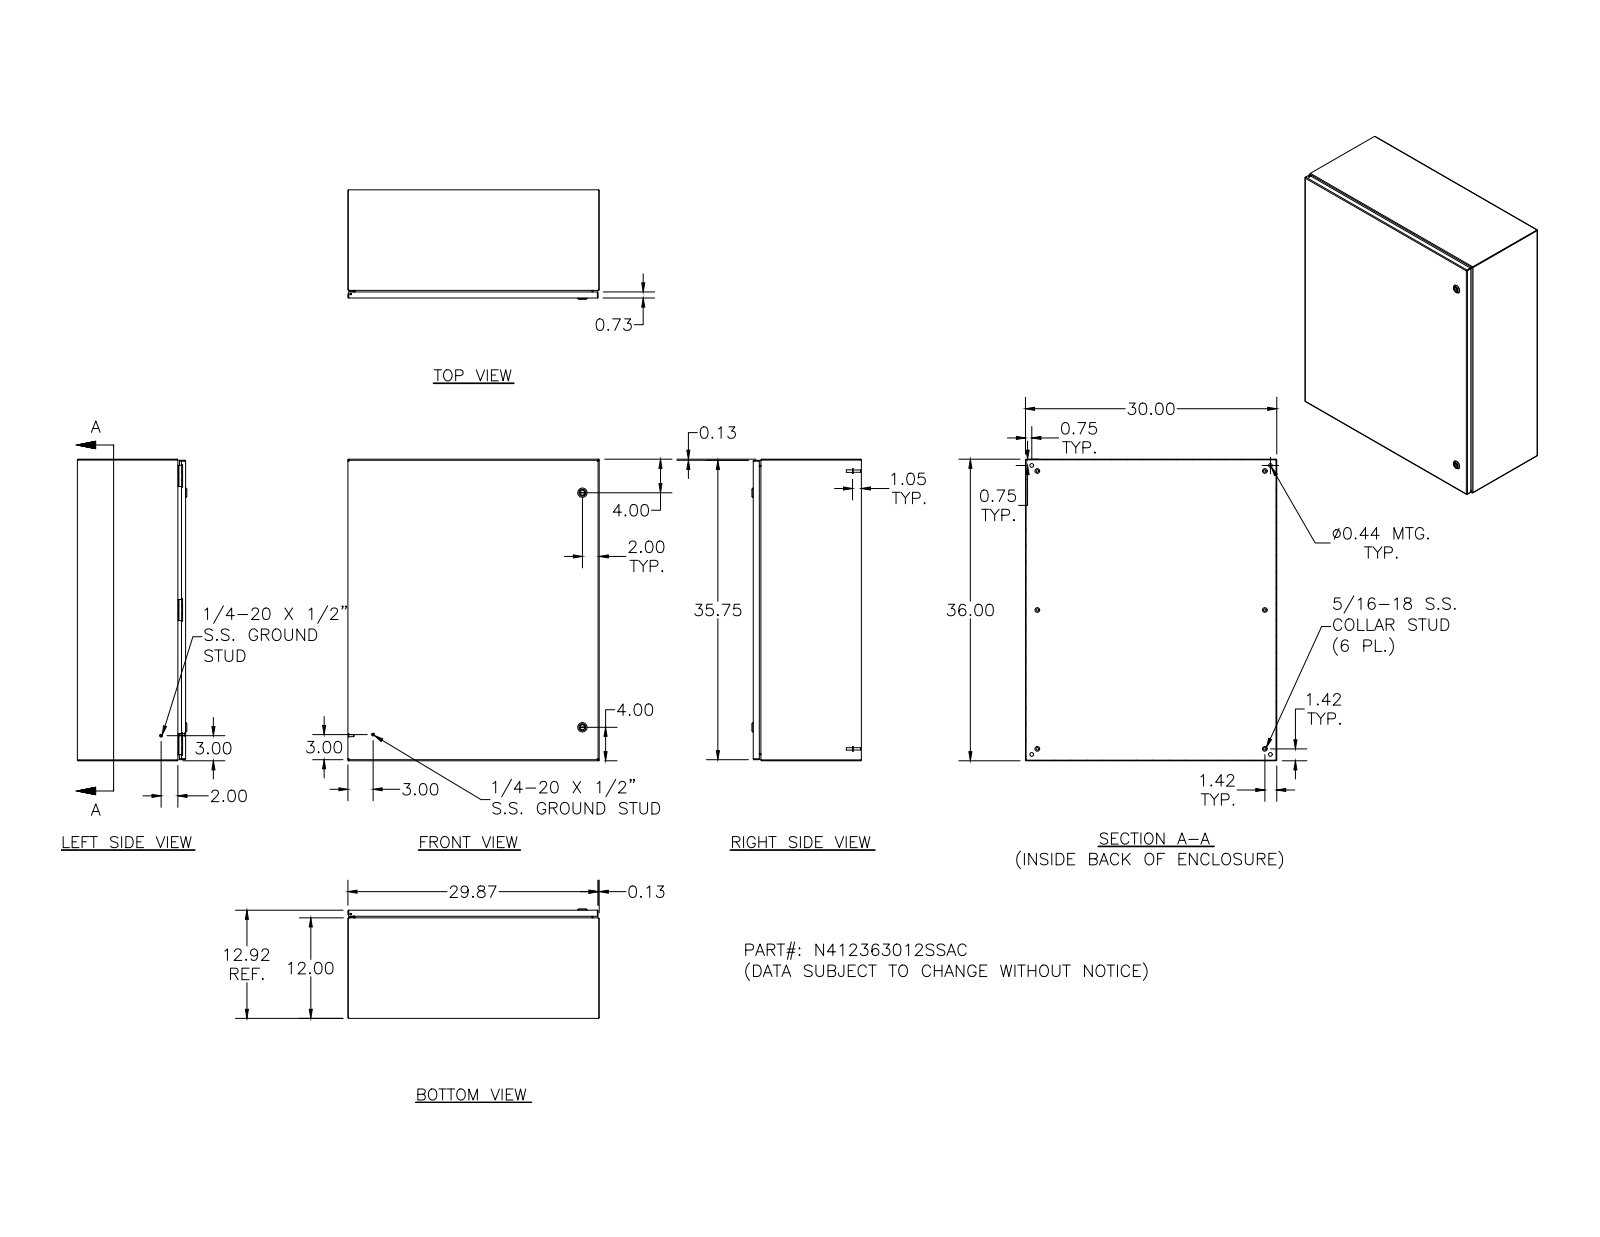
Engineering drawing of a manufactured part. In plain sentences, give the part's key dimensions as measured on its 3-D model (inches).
The part is named "N412363012SSAC; N412363012SSACBKP; 388151; N4123630SSACLID (+8 more)". Its 3-D file was written by "Autodesk Inventor 2011 (AUTOMOTIVE_DESIGN)". It is 53 solids with 2098 faces: 823 planar, 766 cylindrical and 509 other. Overall it measures 36 by 30 by 13.075 inches. Its volume is 297.5 cubic inches and its surface area 8 069 square inches. Round holes: 7 of diameter 0.188, 6 of diameter 0.093, 6 of diameter 0.152, 6 of diameter 0.167, 6 of diameter 0.172, 4 of diameter 0.437, 3 of diameter 0.156, 2 of diameter 0.197, 2 of diameter 0.315, 2 of diameter 0.394, 2 of diameter 0.402, 2 of diameter 0.634. Round bosses or shafts: 14 of diameter 0.25, 6 of diameter 0.563, 6 of diameter 0.36, 6 of diameter 0.32, 6 of diameter 0.3, 6 of diameter 0.275, 6 of diameter 0.256, 6 of diameter 0.164. Partial cylindrical surfaces (rounded edges, fillets, slot ends): 38 of radius 0.05, 26 of radius 0.016, 21 of radius 0.125, 18 of radius 0.031, 16 of radius 0.016, 16 of radius 0.09, 15 of radius 0.02, 12 of radius 0.032. The main face-to-face distances are 0.074, 12.843, 12.769, 12.917, 29.926, 35.926, 29.852, 30, 36, 35.852. The hole center spacings are 16.004, 32, 15.996, 0.017, 0.66, 15.992, 16, 16.008.
